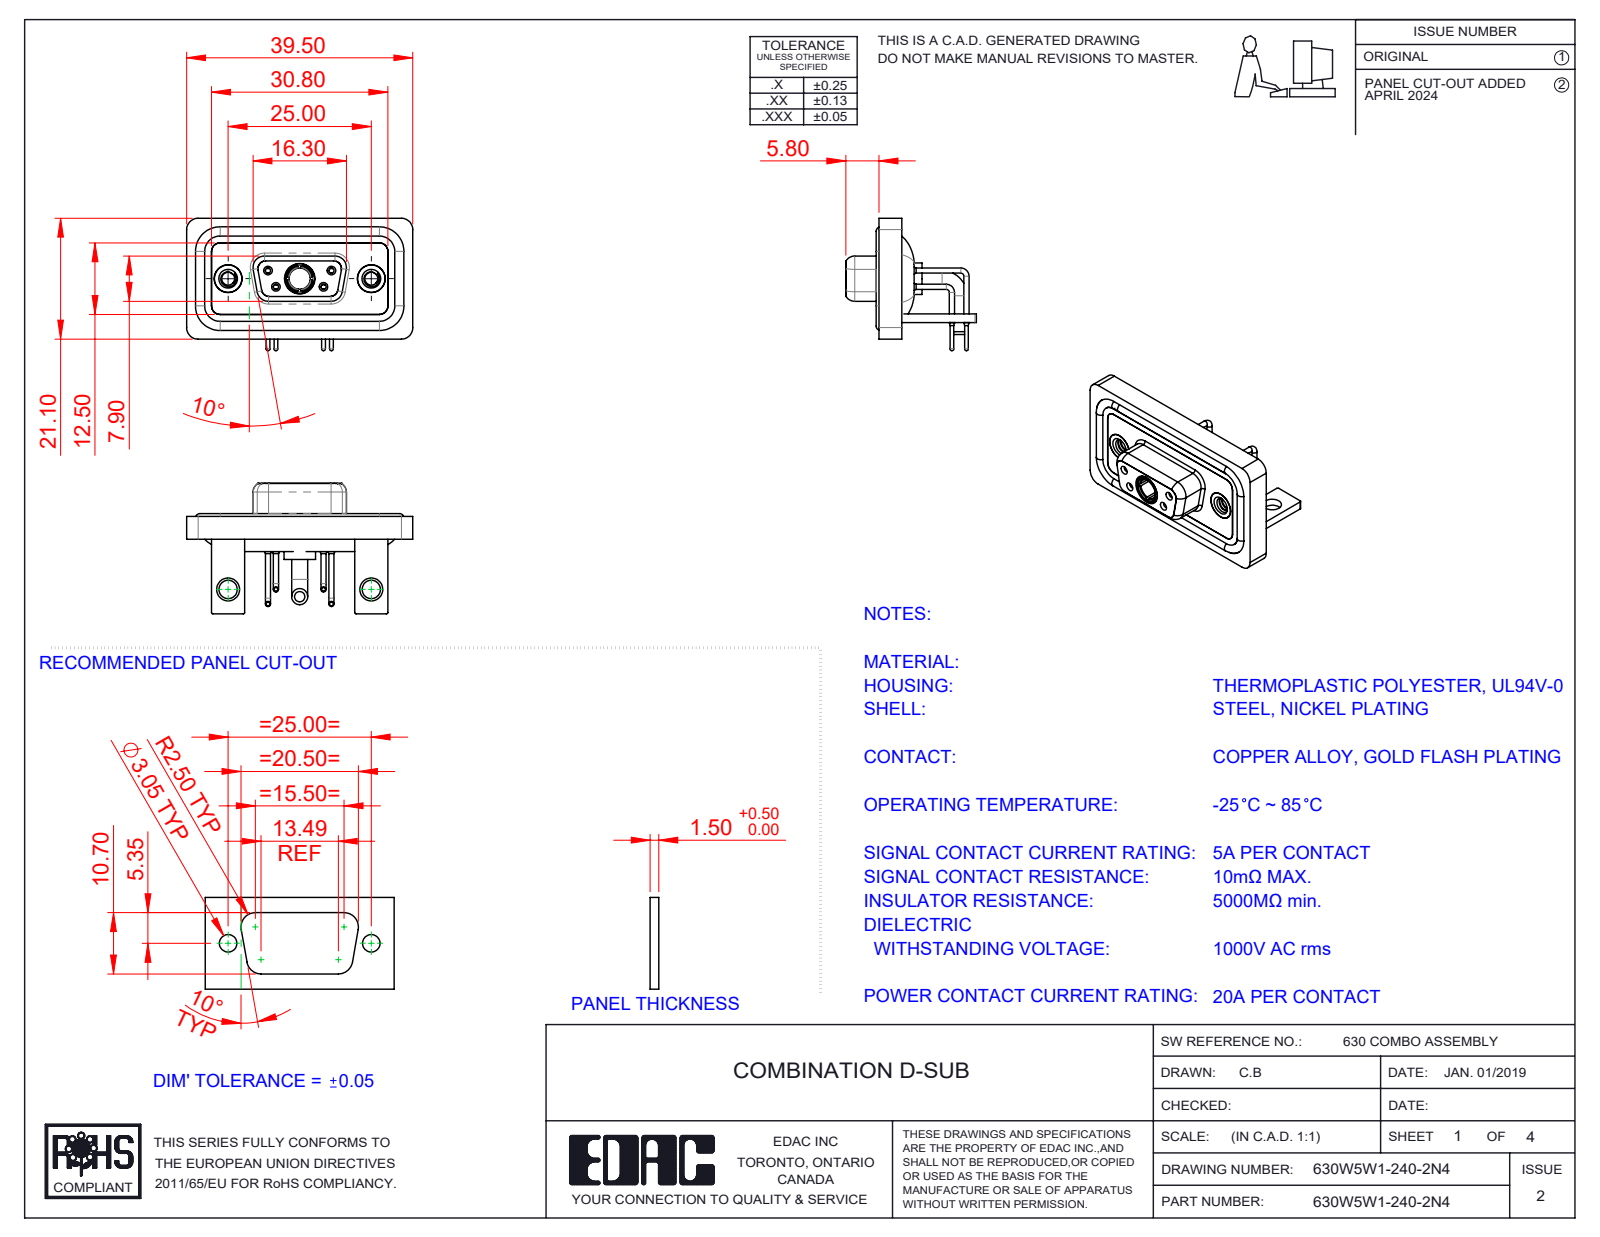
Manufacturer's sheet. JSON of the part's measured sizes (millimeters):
{"part_name": "630Combo Shell Rear_09 Contacts; 630Combo Stabilizer Bracket_50 Contacts; Power Socket_20A RA; 630Combo Housing_5W1 (+6 more)", "step_written_by": "SolidWorks 2023 (CONFIG_CONTROL_DESIGN)", "units": "millimeters", "bodies": {"solids": 15, "faces": 724, "planar": 214, "cylindrical": 329, "other": 181}, "overall_size": [39.5, 23.12, 22.8], "volume_mm3": 5195, "surface_area_mm2": 8579, "round_holes": [[0.9, 4], [1.1, 4], [1.5, 4], [2, 4], [4.85, 3], [1.6, 2], [1.7, 2], [2.26, 2], [3.2, 2], [4, 2], [4.05, 2], [5, 2]], "round_bosses_or_shafts": [[1.6, 6], [0.9, 4], [0.65, 4], [4.95, 2], [4.8, 2], [2.8, 2], [5.5, 1], [5.2, 1]], "partial_cylinders_radius": [[2, 19], [1.5, 18], [0.25, 16], [1.35, 8], [1.6, 8], [0.5, 5], [0.6, 4], [0.65, 4]], "face_to_face_distances": [0.4, 2.9, 1.5, 1.8, 1.1, 3.7, 1.6, 0.8, 2.5, 3.1], "hole_center_spacings": [3.16, 5.72, 7.1, 12.5, 18.1, 25, 4.39, 4.4]}
